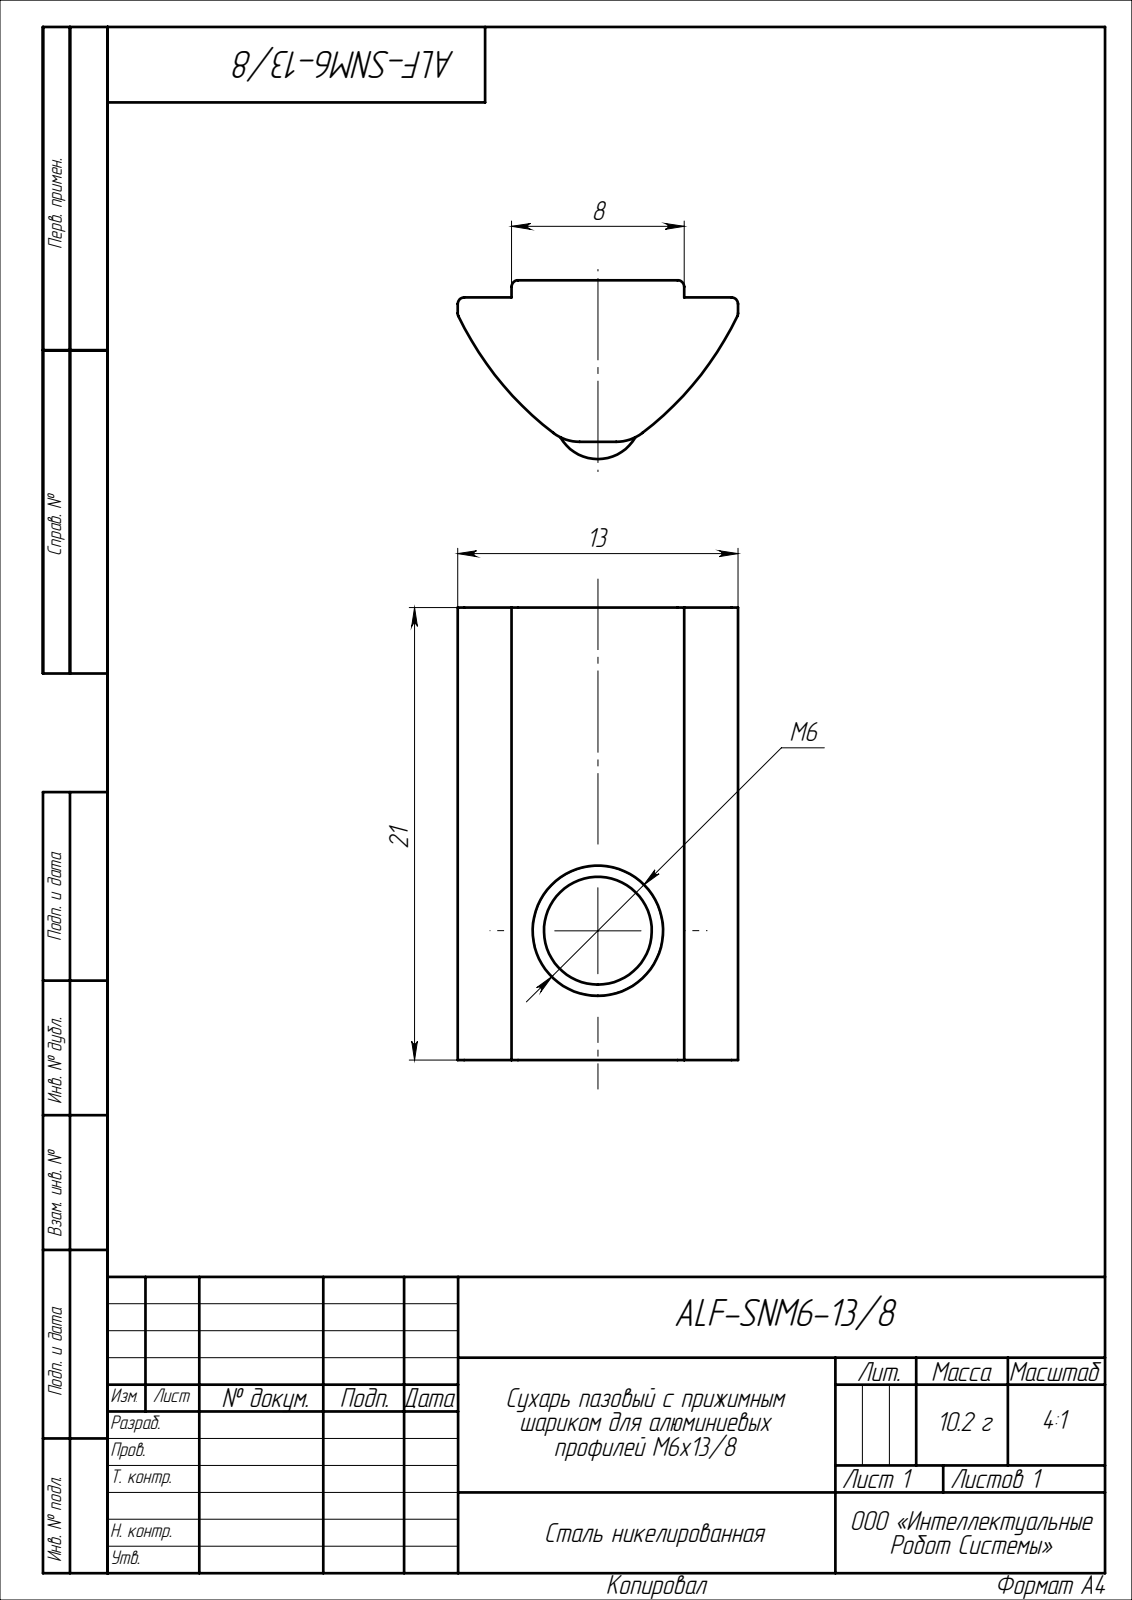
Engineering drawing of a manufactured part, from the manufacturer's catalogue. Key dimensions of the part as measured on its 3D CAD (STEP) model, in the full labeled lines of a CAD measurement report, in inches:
Part name (STEP PRODUCT): ALF-SNM6-13_8
STEP written by: SolidWorks 2022 (CONFIG_CONTROL_DESIGN)
Units: inches
Bodies: 1 solid, 30 faces (12 planar, 14 cylindrical, 4 other)
Overall size (bounding box): 0.827 × 0.512 × 0.327
Volume: 0.08 in³ · Surface area: 1.44 in²
Round holes (diameter × count): ⌀0.197 ×1
Partial cylindrical surfaces — rounded edges, fillets, slot ends (radius × count): R0.012 ×6, R0.079 ×2, R0.591 ×2
Main face-to-face distances: 0.031, 0.827, 0.264, 0.295, 0.098, 0.413, 0.315, 0.512
